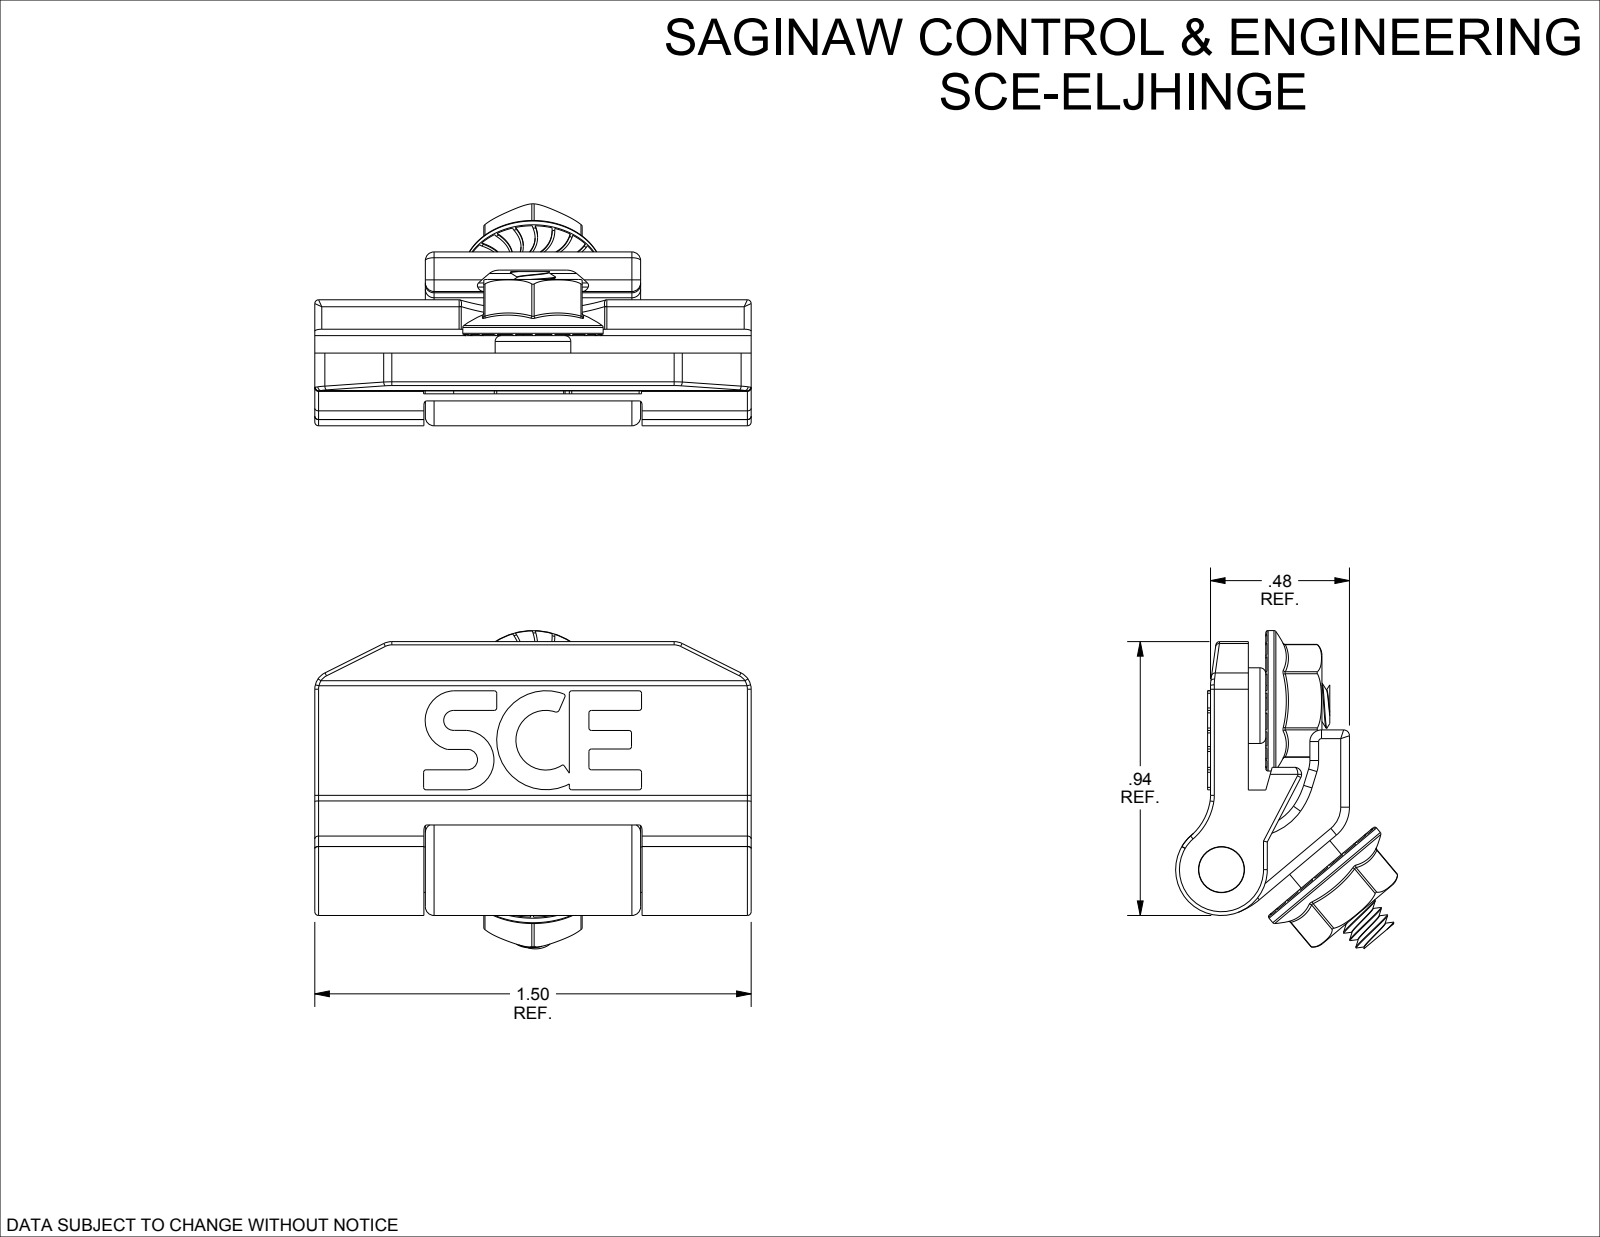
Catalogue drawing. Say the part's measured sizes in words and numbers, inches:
The part is named "SCE-ELJHINGE". Its 3-D file was written by "SolidWorks 2019 (AUTOMOTIVE_DESIGN)". It is 7 solids with 407 faces: 145 planar, 83 cylindrical and 179 other. Overall it measures 1.5 by 1.087 by 0.763 inches. Its volume is 0.392 cubic inches and its surface area 8.901 square inches. Round holes: 2 of diameter 0.16, 1 of diameter 0.02, 1 of diameter 0.1, 1 of diameter 0.158. Round bosses or shafts: 2 of diameter 0.483, 2 of diameter 0.237, 2 of diameter 0.16, 1 of diameter 0.315, 1 of diameter 0.26, 1 of diameter 0.18, 1 of diameter 0.156. Partial cylindrical surfaces (rounded edges, fillets, slot ends): 12 of radius 0.008, 12 of radius 0.03, 11 of radius 0.013, 3 of radius 0.024, 3 of radius 0.062, 3 of radius 0.125, 2 of radius 0.01, 2 of radius 0.015. The main face-to-face distances are 0.13, 0.38, 1.12, 0.348, 0.478, 1.5, 0.283, 0.064, 0.194, 0.066.
